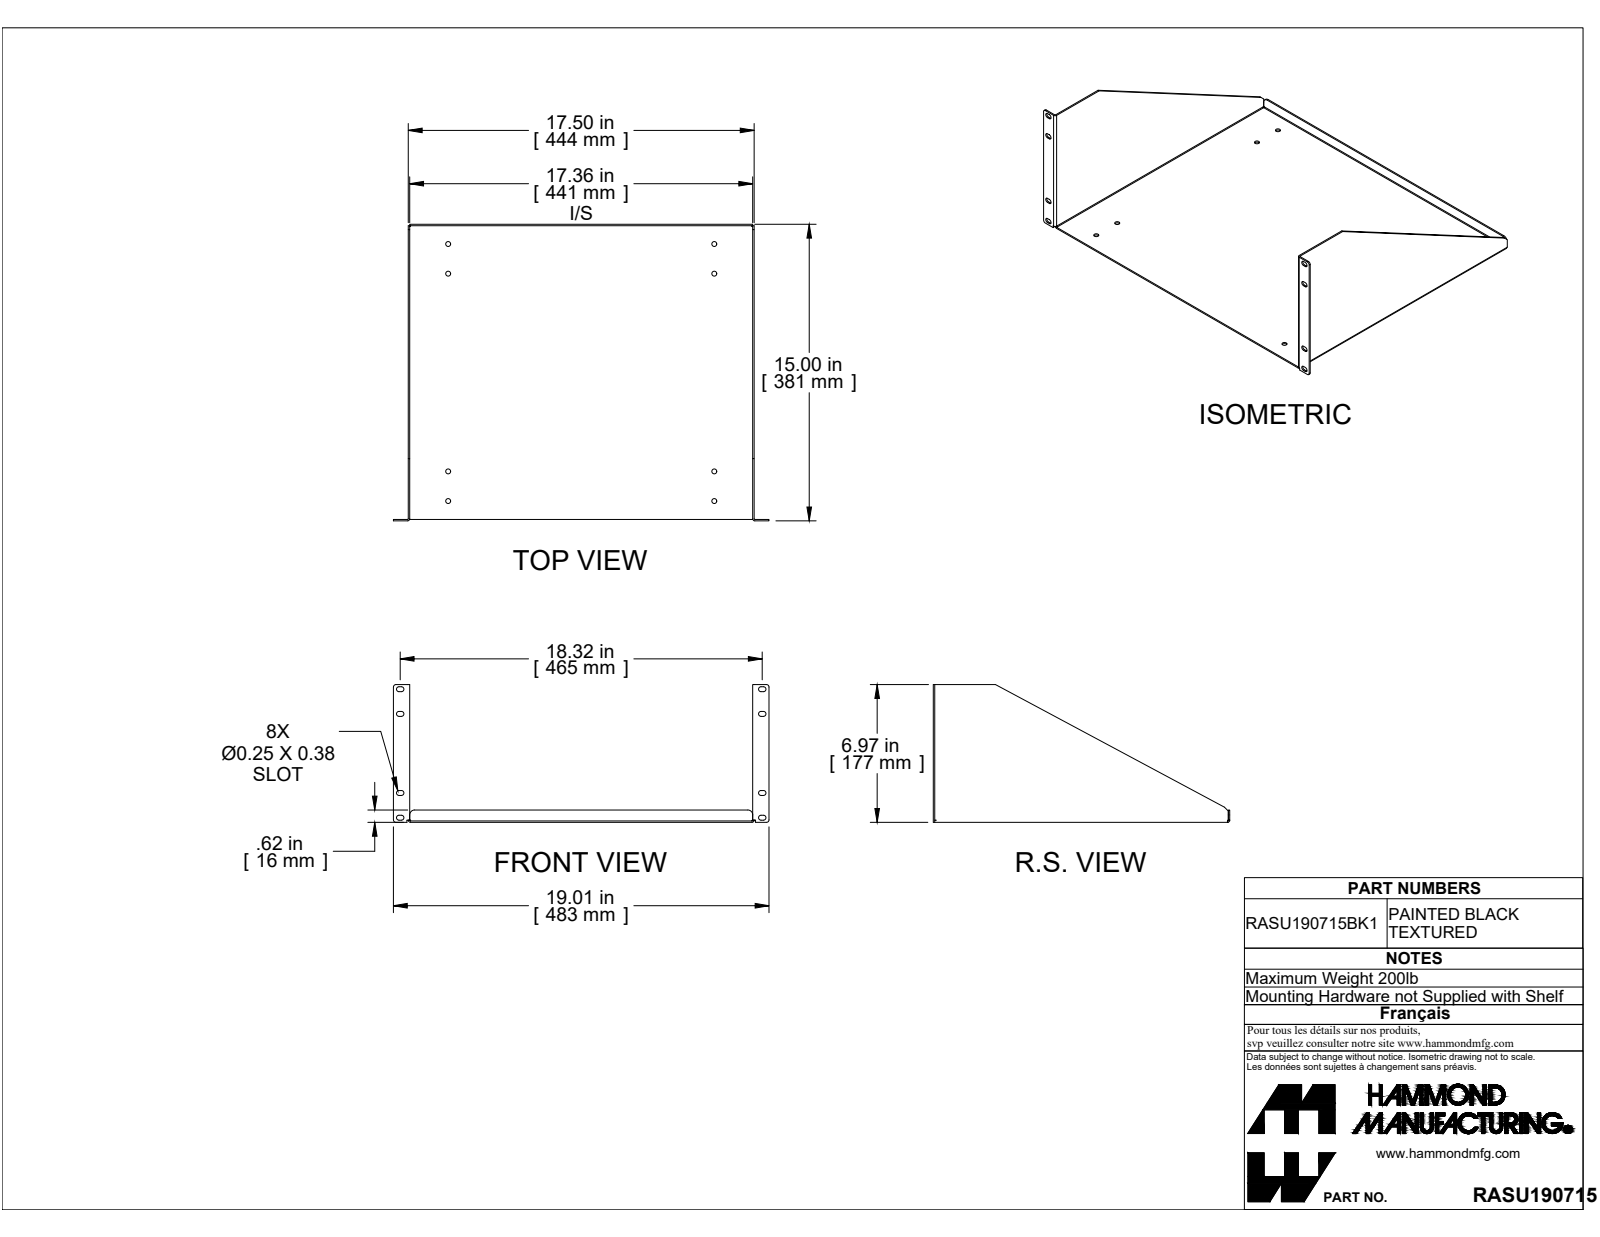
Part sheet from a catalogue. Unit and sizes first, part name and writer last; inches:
Units: inches
Overall size (bounding box): 19.006 × 15 × 6.968
Round holes (diameter × count): ⌀0.25 ×8
Partial cylindrical surfaces — rounded edges, fillets, slot ends (radius × count): R0.125 ×20, R0.036 ×5, R0.108 ×5, R0.055 ×3, R0.25 ×2
Main face-to-face distances: 0.072, 17.428, 17.356, 17.5, 0.072, 15, 14.928, 14.928, 14.856, 0.625
Hole centre spacings: 1.5, 11.5, 13.468, 13.551, 17.709, 10, 13, 16.774
Volume: 29.51 in³ · Surface area: 827.2 in²
Bodies: 1 solid, 104 faces (56 planar, 44 cylindrical, 4 other)
Part name (STEP PRODUCT): RASU190715BK1
STEP written by: SolidWorks 2019 (CONFIG_CONTROL_DESIGN)
